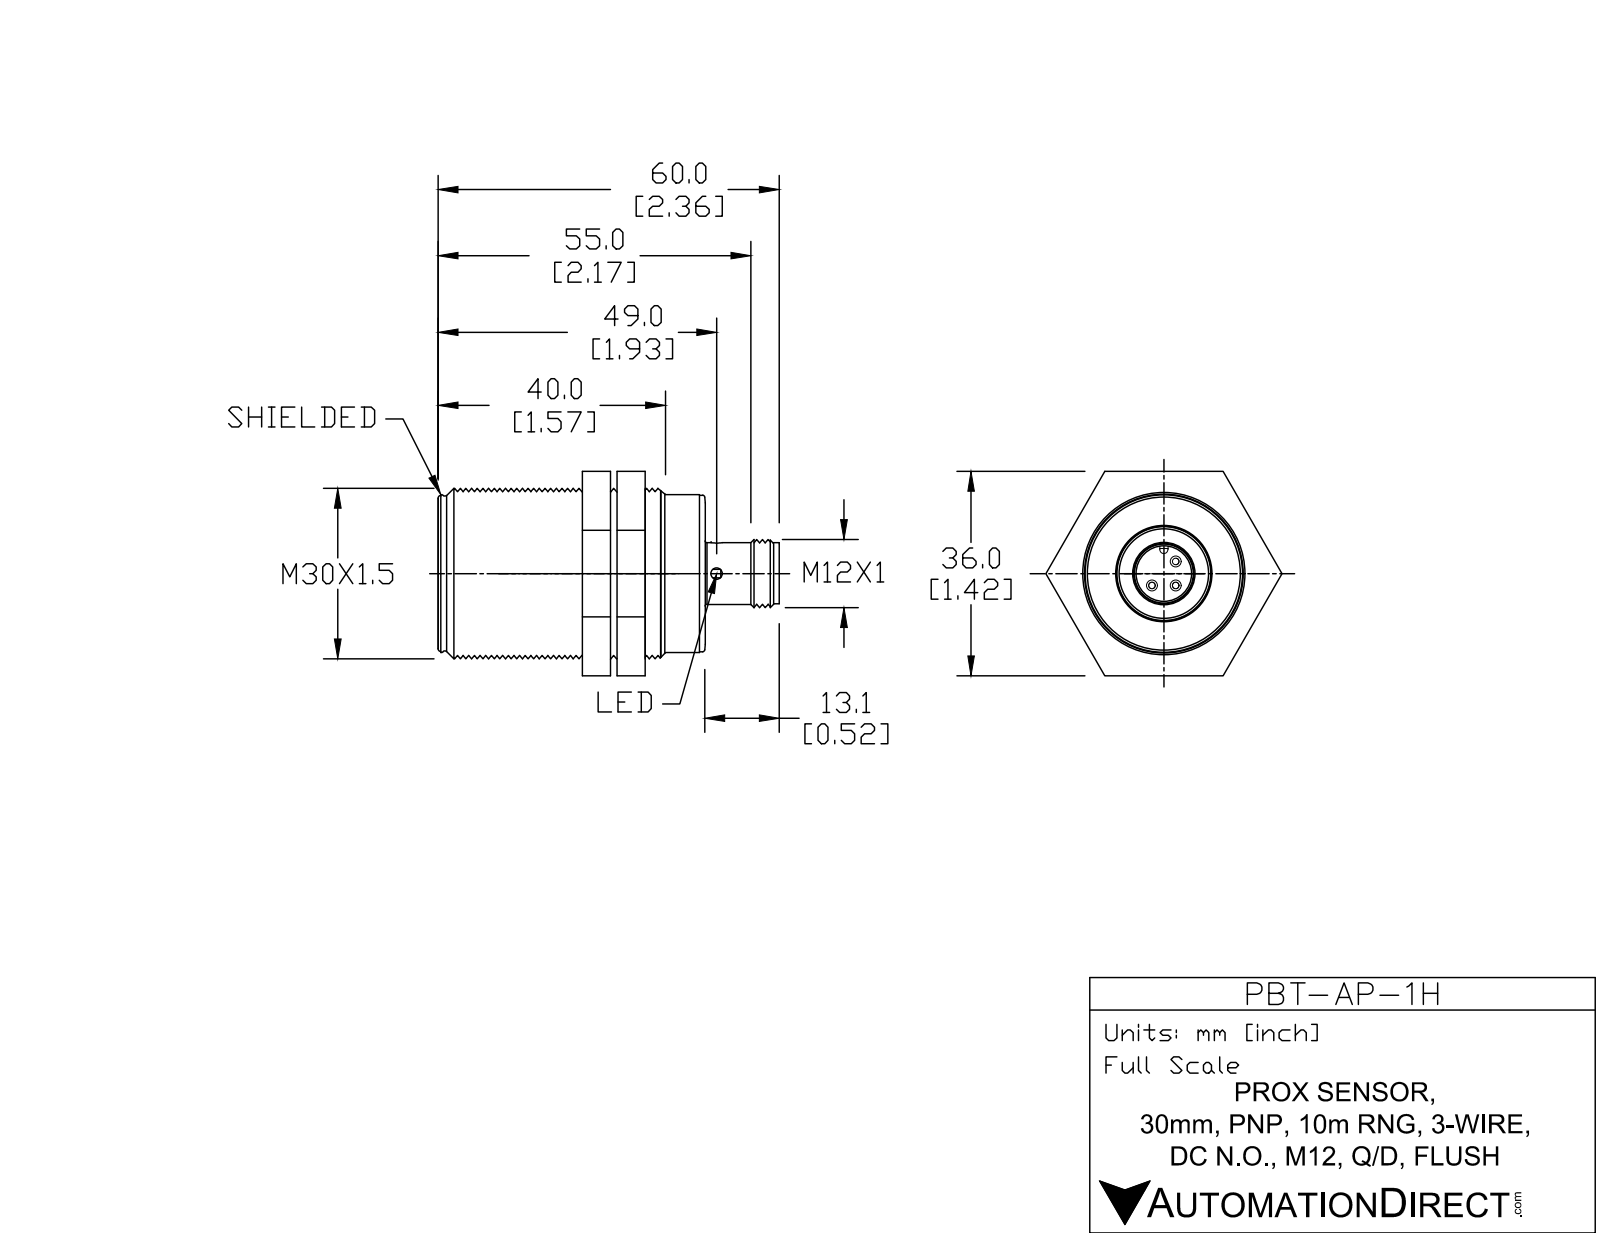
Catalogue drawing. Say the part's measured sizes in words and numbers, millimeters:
The part is named "PBT-AP-1H". Its 3-D file was written by "SolidWorks 2011 (AUTOMOTIVE_DESIGN)". It is 8 solids with 68 faces: 39 planar, 18 cylindrical and 11 other. Overall it measures 59.25 by 41.55 by 36.66 millimeters. Its volume is 37 038 cubic millimeters and its surface area 11 781 square millimeters. Round holes: 1 of diameter 1.25, 1 of diameter 8.5, 1 of diameter 10.5, 1 of diameter 28.5. Round bosses or shafts: 3 of diameter 1, 1 of diameter 30, 1 of diameter 28, 1 of diameter 27.5, 1 of diameter 27.46, 1 of diameter 12, 1 of diameter 10.9, 1 of diameter 10.55. Partial cylindrical surfaces (rounded edges, fillets, slot ends): 1 of radius 0.5. The main face-to-face distances are 10, 4.5, 14.5, 0.75, 46, 46.75, 20, 36, 36.75, 26.
